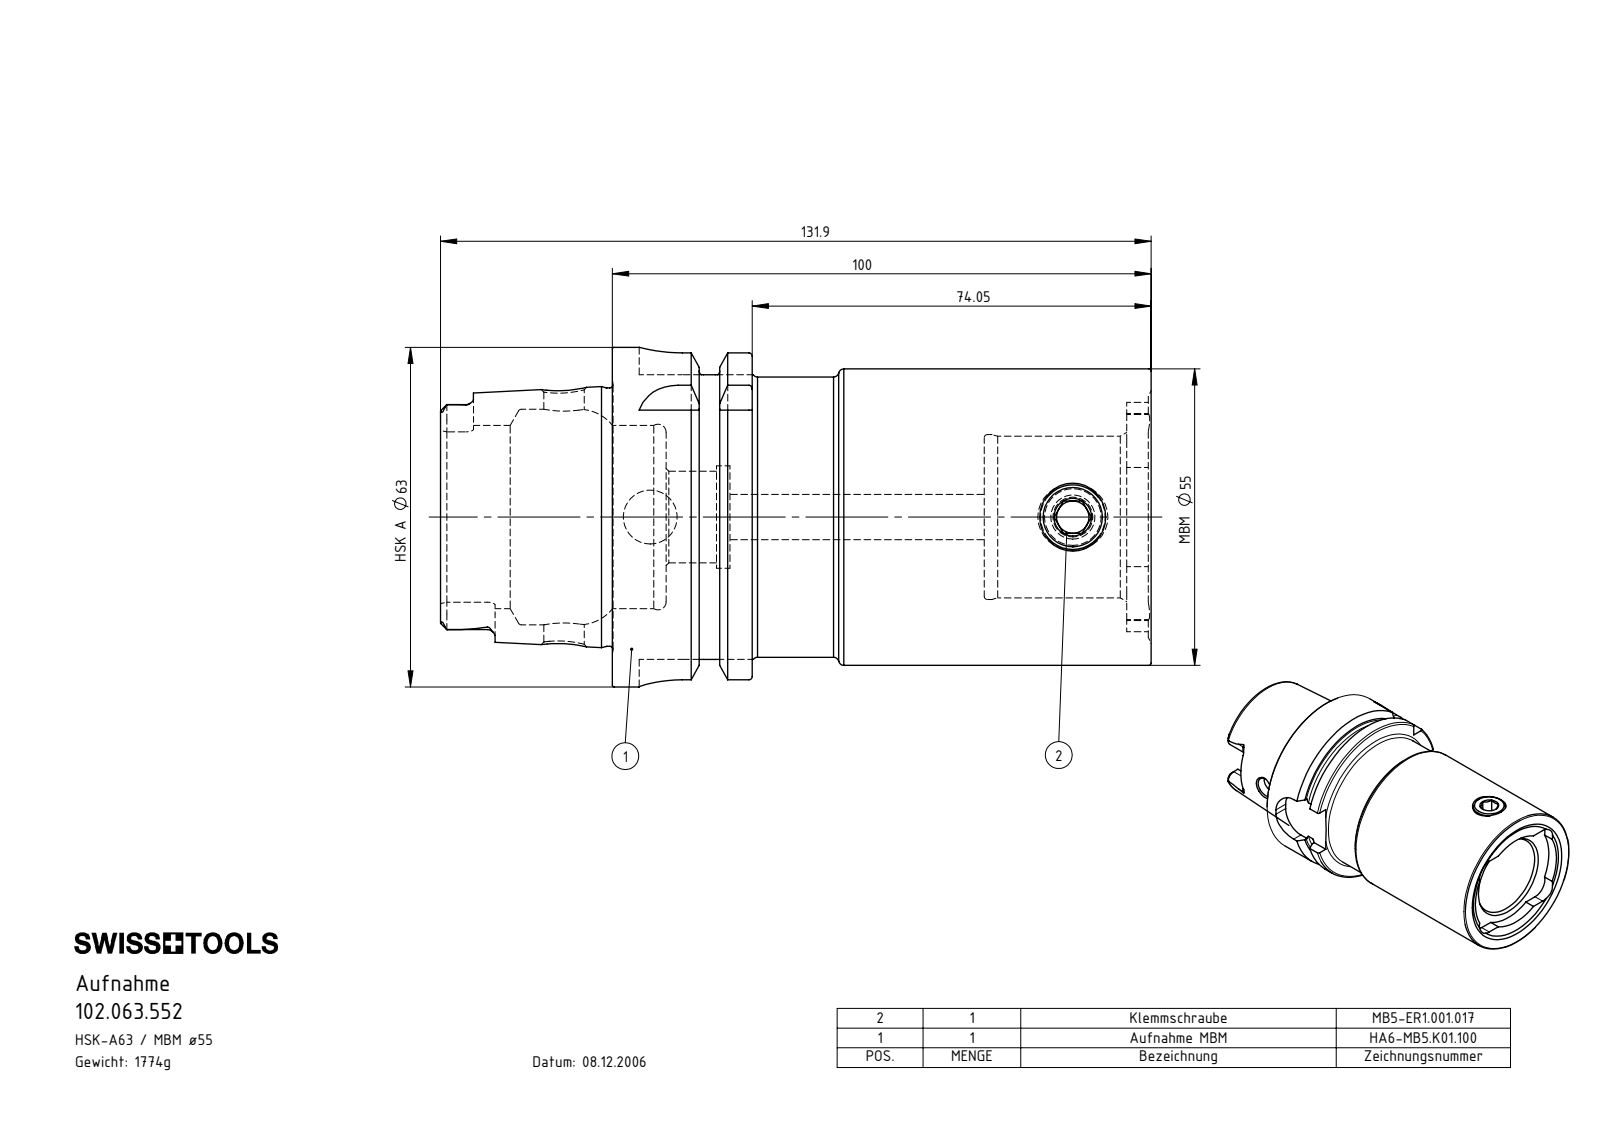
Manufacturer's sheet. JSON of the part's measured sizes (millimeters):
{"part_name": "HA6-MB5.K01.100_A_Fertigbearbeitung; MB5-ER1.001.017_A; 102.063.552", "step_written_by": "SolidWorks 2017 (CONFIG_CONTROL_DESIGN)", "units": "millimeters", "bodies": {"solids": 2, "faces": 230, "planar": 71, "cylindrical": 68, "other": 91}, "overall_size": [131.9, 63, 63], "volume_mm3": 225985, "surface_area_mm2": 40421, "round_holes": [[6, 1], [7.5, 1], [8.4, 1], [10, 1], [11, 1], [17, 1], [19, 1], [30, 1], [30.6, 1], [34, 1], [40, 1]], "round_bosses_or_shafts": [[63, 1], [55, 1], [54.95, 1], [52, 1], [47.93, 1], [12, 1]], "partial_cylinders_radius": [[1.4, 6], [2.88, 4], [5.2, 4], [8, 4], [18.5, 1], [21.27, 1]], "face_to_face_distances": [69, 100, 31, 25.95, 43.05, 74.05, 16, 95.45, 69.5, 26.45], "hole_center_spacings": [78.45]}
